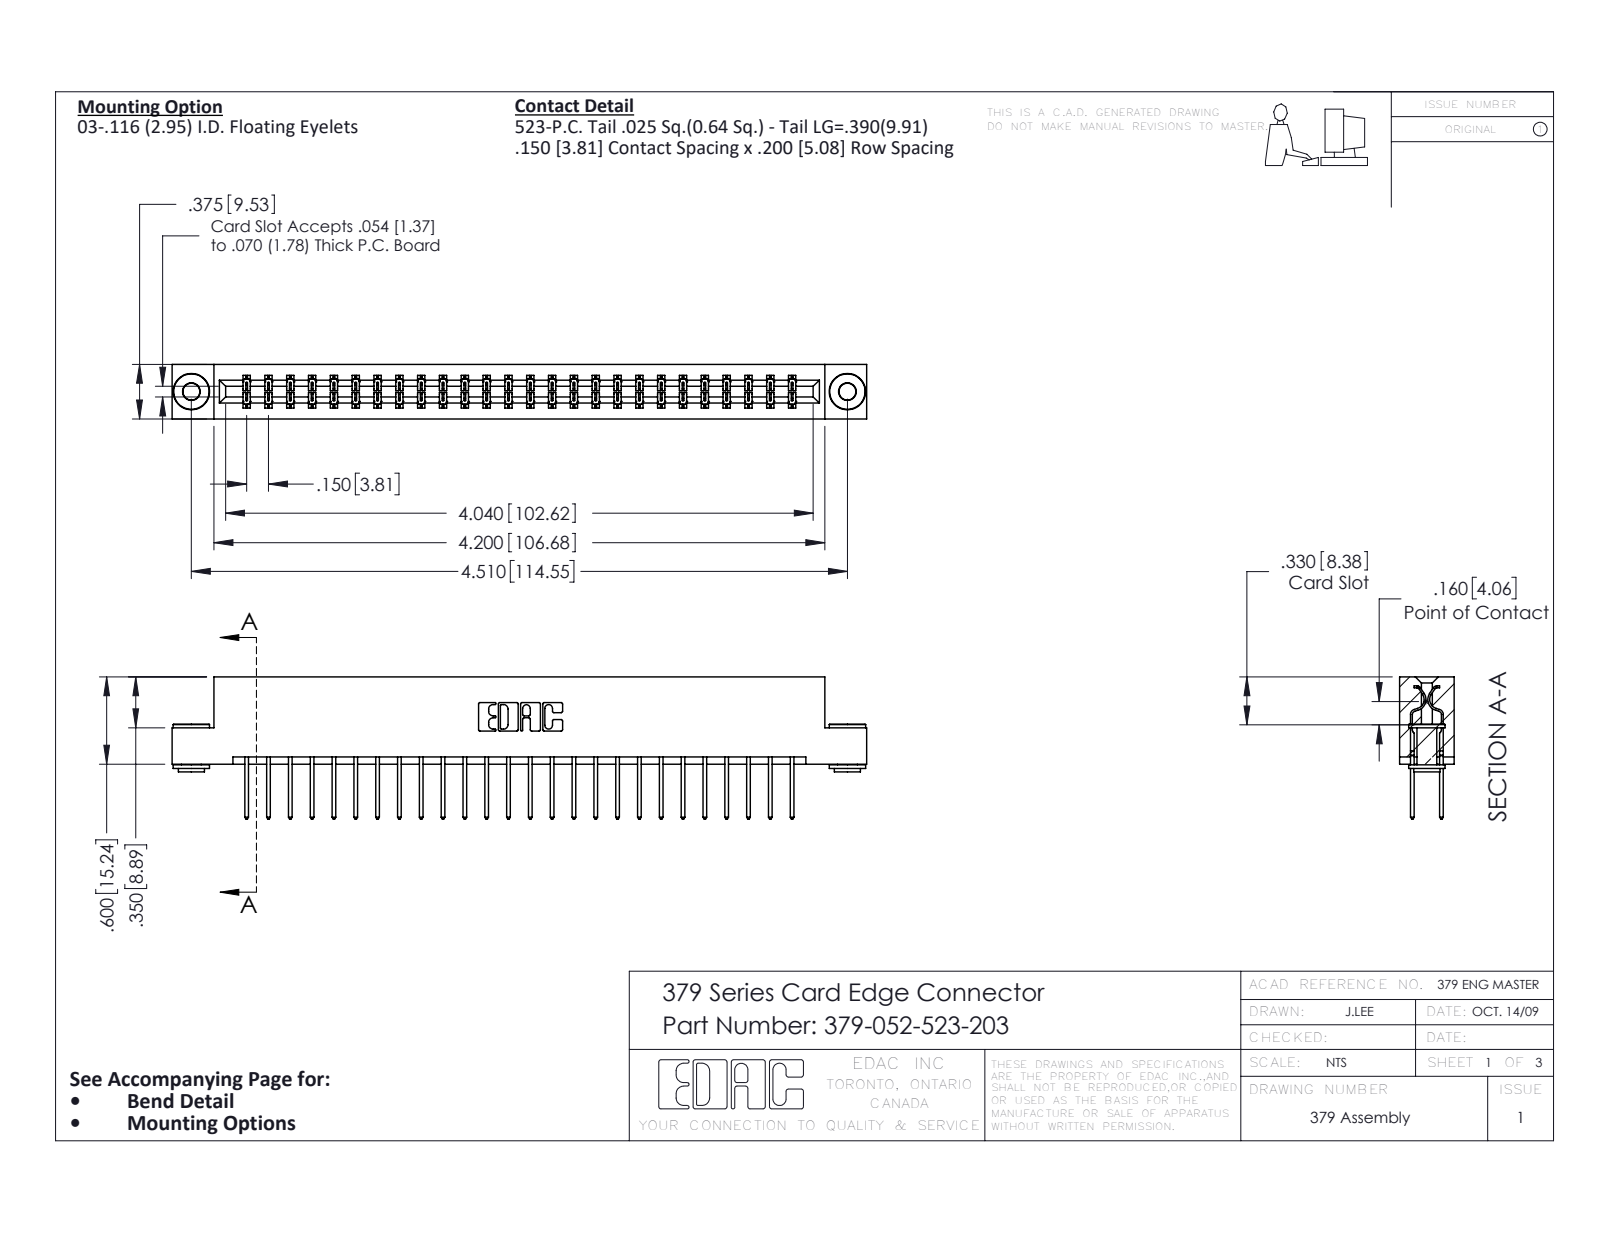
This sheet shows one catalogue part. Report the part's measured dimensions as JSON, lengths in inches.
{"part_name": "379 Part_Flush - .156 Dia - TH; 379-052-523-203; 345-292-001_345-293-123; 345-250-002_345-250-002-102", "step_written_by": "SolidWorks 2016 (CONFIG_CONTROL_DESIGN)", "units": "inches", "bodies": {"solids": 55, "faces": 2856, "planar": 1952, "cylindrical": 896, "other": 8}, "overall_size": [4.775, 0.977, 0.375], "volume_in3": 0.784, "surface_area_in2": 23.27, "round_holes": [[0.116, 2], [0.156, 2]], "round_bosses_or_shafts": [[0.25, 2], [0.18, 2], [0.136, 2]], "partial_cylinders_radius": [[0.006, 78], [0.01, 52], [0.01, 22], [0.007, 6], [0.031, 6], [0.026, 3], [0.014, 2], [0.022, 2]], "face_to_face_distances": [0.3, 0.075, 0.375, 0.2, 0.1, 0.275, 0.025, 0.225, 0.15, 0.076], "hole_center_spacings": [4.51]}
